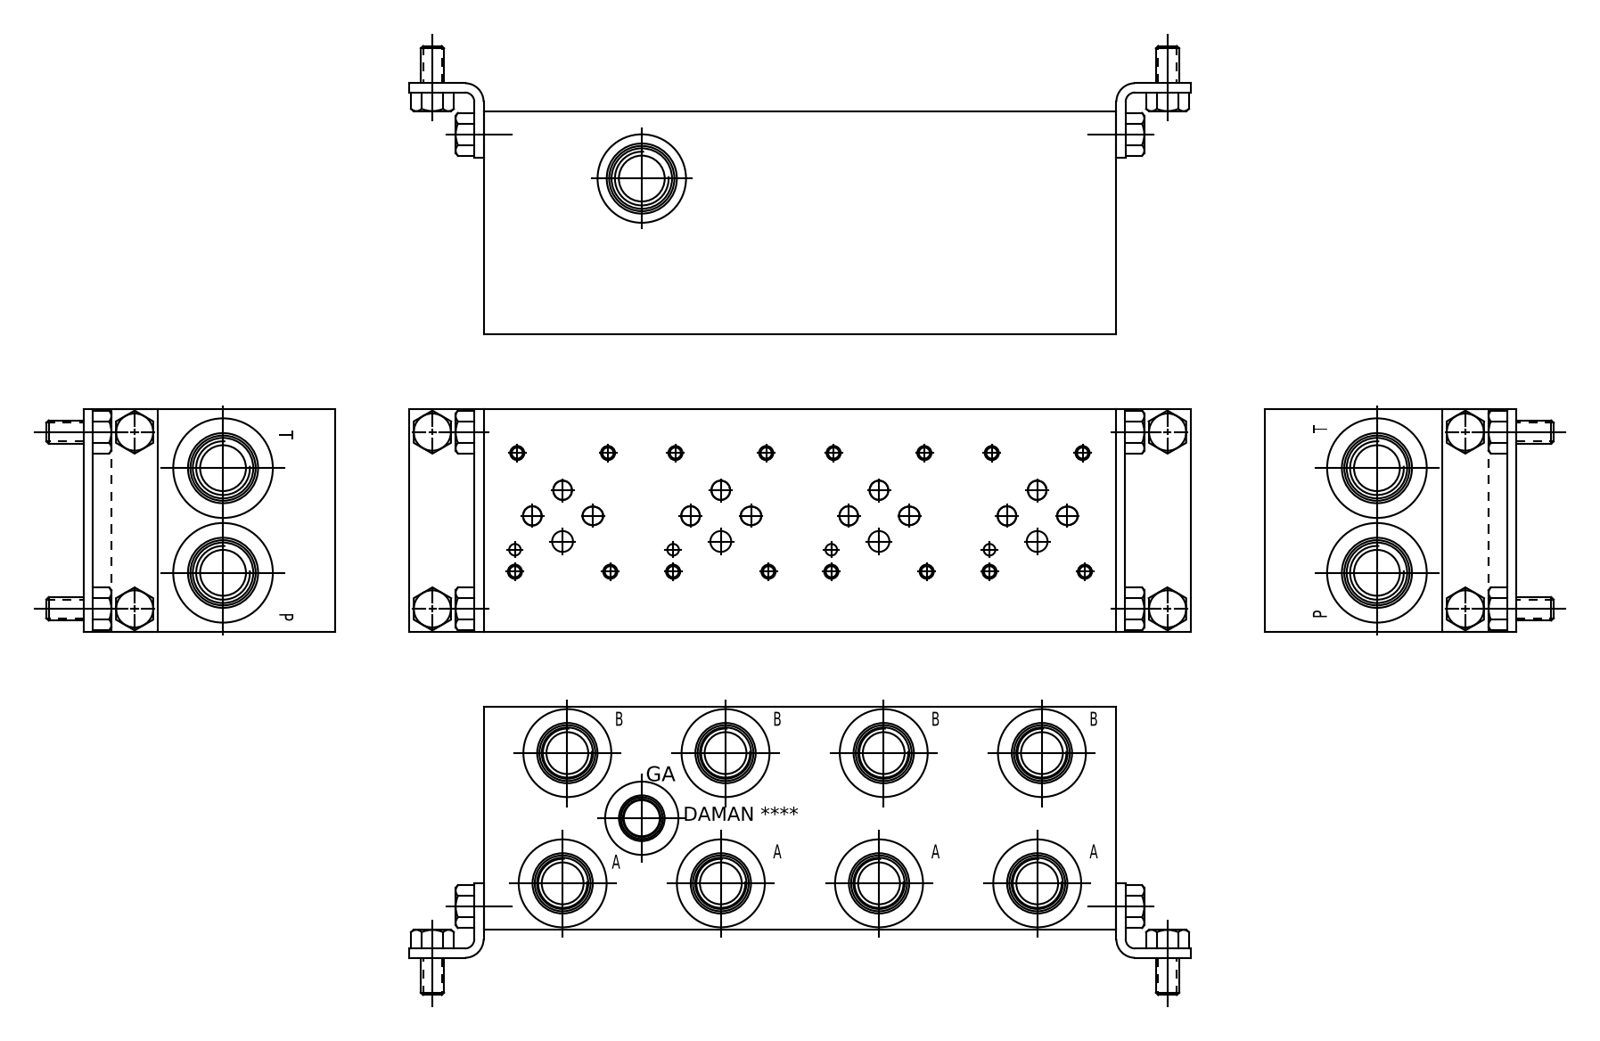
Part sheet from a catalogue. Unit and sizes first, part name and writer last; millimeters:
Units: millimetres
Overall size (bounding box): 215.9 × 76.2 × 76.2
Round holes (diameter × count): ⌀3.78 ×16, ⌀4.83 ×16, ⌀6.35 ×12, ⌀14.3 ×9, ⌀17.5 ×8, ⌀19.05 ×8, ⌀19.25 ×8, ⌀30.63 ×8, ⌀3.96 ×4, ⌀7.14 ×4, ⌀6.53 ×2, ⌀7.92 ×2
Main face-to-face distances: 76.2, 0.79, 215.9, 75.41, 215.11, 214.32, 15.06, 14.27, 61.14, 0.75
Hole centre spacings: 107.95, 53.98, 53.97, 56.73, 22.05, 33.55, 51.45, 161.93
Volume: 1 134 000 mm³ · Surface area: 105 783 mm²
Bodies: 1 solid, 873 faces (435 planar, 134 cylindrical, 304 other)
Part name (STEP PRODUCT): Part_AD03S042S_C_3D
STEP written by: Autodesk Inventor 2020 (AUTOMOTIVE_DESIGN)
